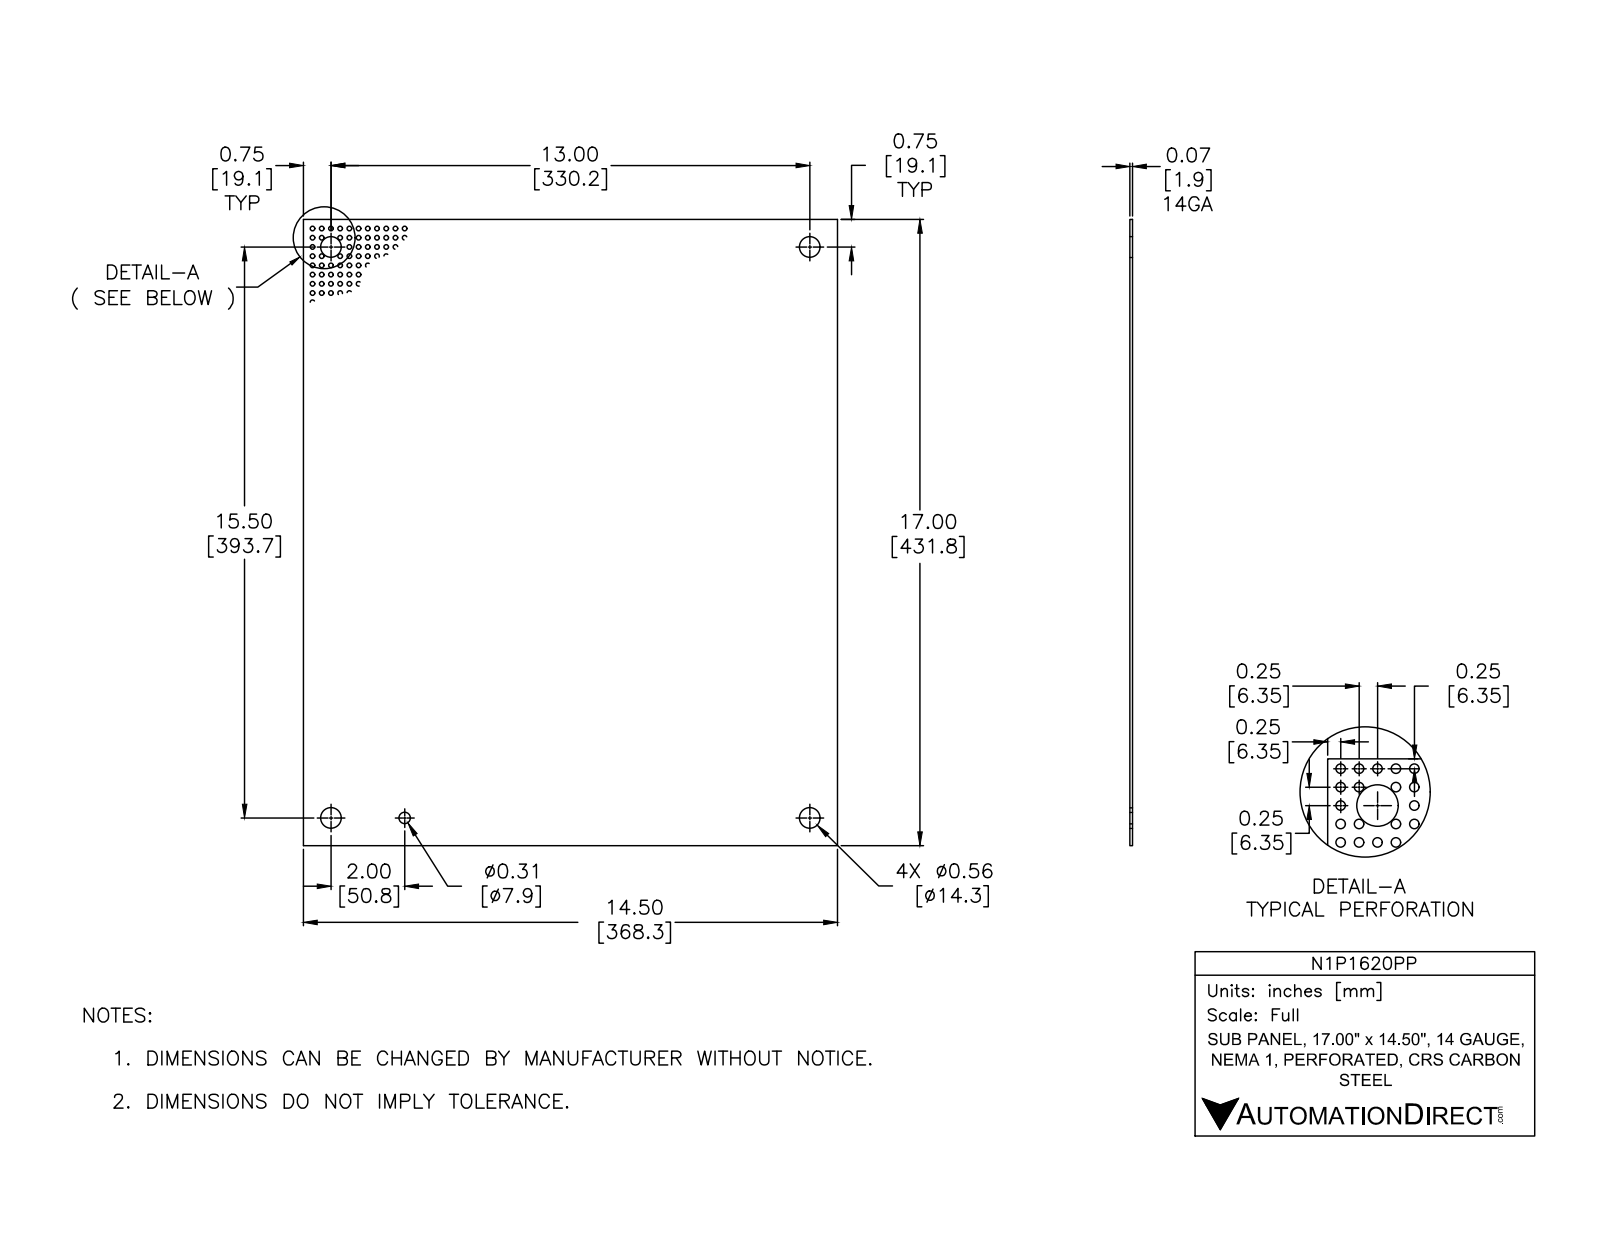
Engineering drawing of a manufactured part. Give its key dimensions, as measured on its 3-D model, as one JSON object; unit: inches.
{"part_name": "N1P_PP-LARGE", "step_written_by": "Autodesk Inventor 2012 (AUTOMOTIVE_DESIGN)", "units": "inches", "bodies": {"solids": 1, "faces": 11, "planar": 6, "cylindrical": 5, "other": 0}, "overall_size": [17, 14.5, 0.074], "volume_in3": 18.16, "surface_area_in2": 496.1, "round_holes": [[0.563, 4], [0.312, 1]], "face_to_face_distances": [0.074, 14.5, 17], "hole_center_spacings": [13, 15.5, 20.23, 2, 11, 15.628, 19.007]}
